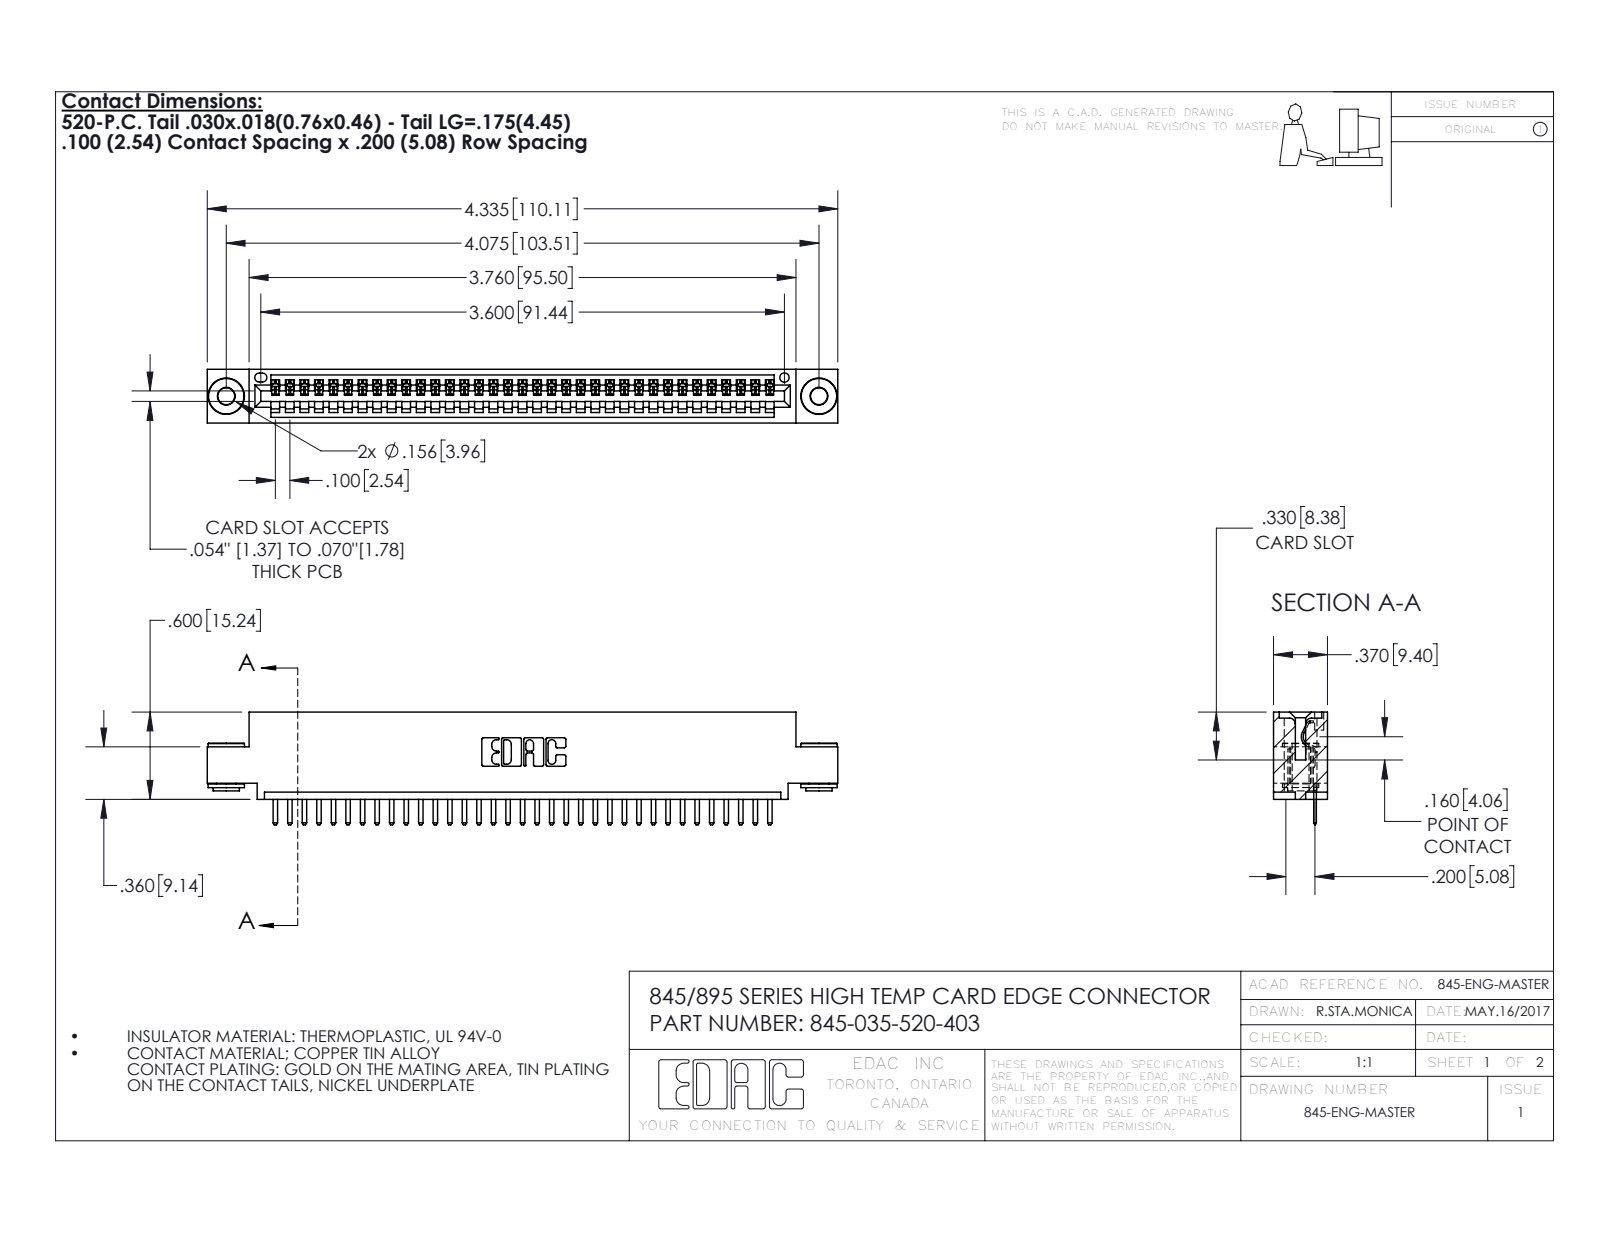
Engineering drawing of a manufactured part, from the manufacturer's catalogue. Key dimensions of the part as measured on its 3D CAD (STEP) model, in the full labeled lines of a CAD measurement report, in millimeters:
Part name (STEP PRODUCT): 345-035-520-403; 345-292-001_345-293-120; 345 Part_0.110 Offset - 0.156 Dia-TH; 345-250-002_345-250-002-102
STEP written by: SolidWorks 2016 (CONFIG_CONTROL_DESIGN)
Units: millimetres
Bodies: 38 solids, 2338 faces (1564 planar, 766 cylindrical, 8 other)
Overall size (bounding box): 110.1 × 19.7 × 9.4
Volume: 10 200 mm³ · Surface area: 13 490 mm²
Round holes (diameter × count): ⌀2.9 ×2, ⌀4 ×2, ⌀1.6 ×1
Round bosses / shafts (diameter × count): ⌀6.4 ×2, ⌀4.6 ×2, ⌀3.5 ×2
Partial cylindrical surfaces — rounded edges, fillets, slot ends (radius × count): R0.3 ×72, R0.2 ×70, R0.3 ×22, R0.2 ×6, R0.8 ×6, R0.7 ×3, R0.8 ×2, R1 ×2
Main face-to-face distances: 1.8, 7.6, 9.4, 5.1, 0.6, 2.5, 6.9, 5.7, 1.8, 3.8
Hole centre spacings: 6.9, 97.5, 103.5
